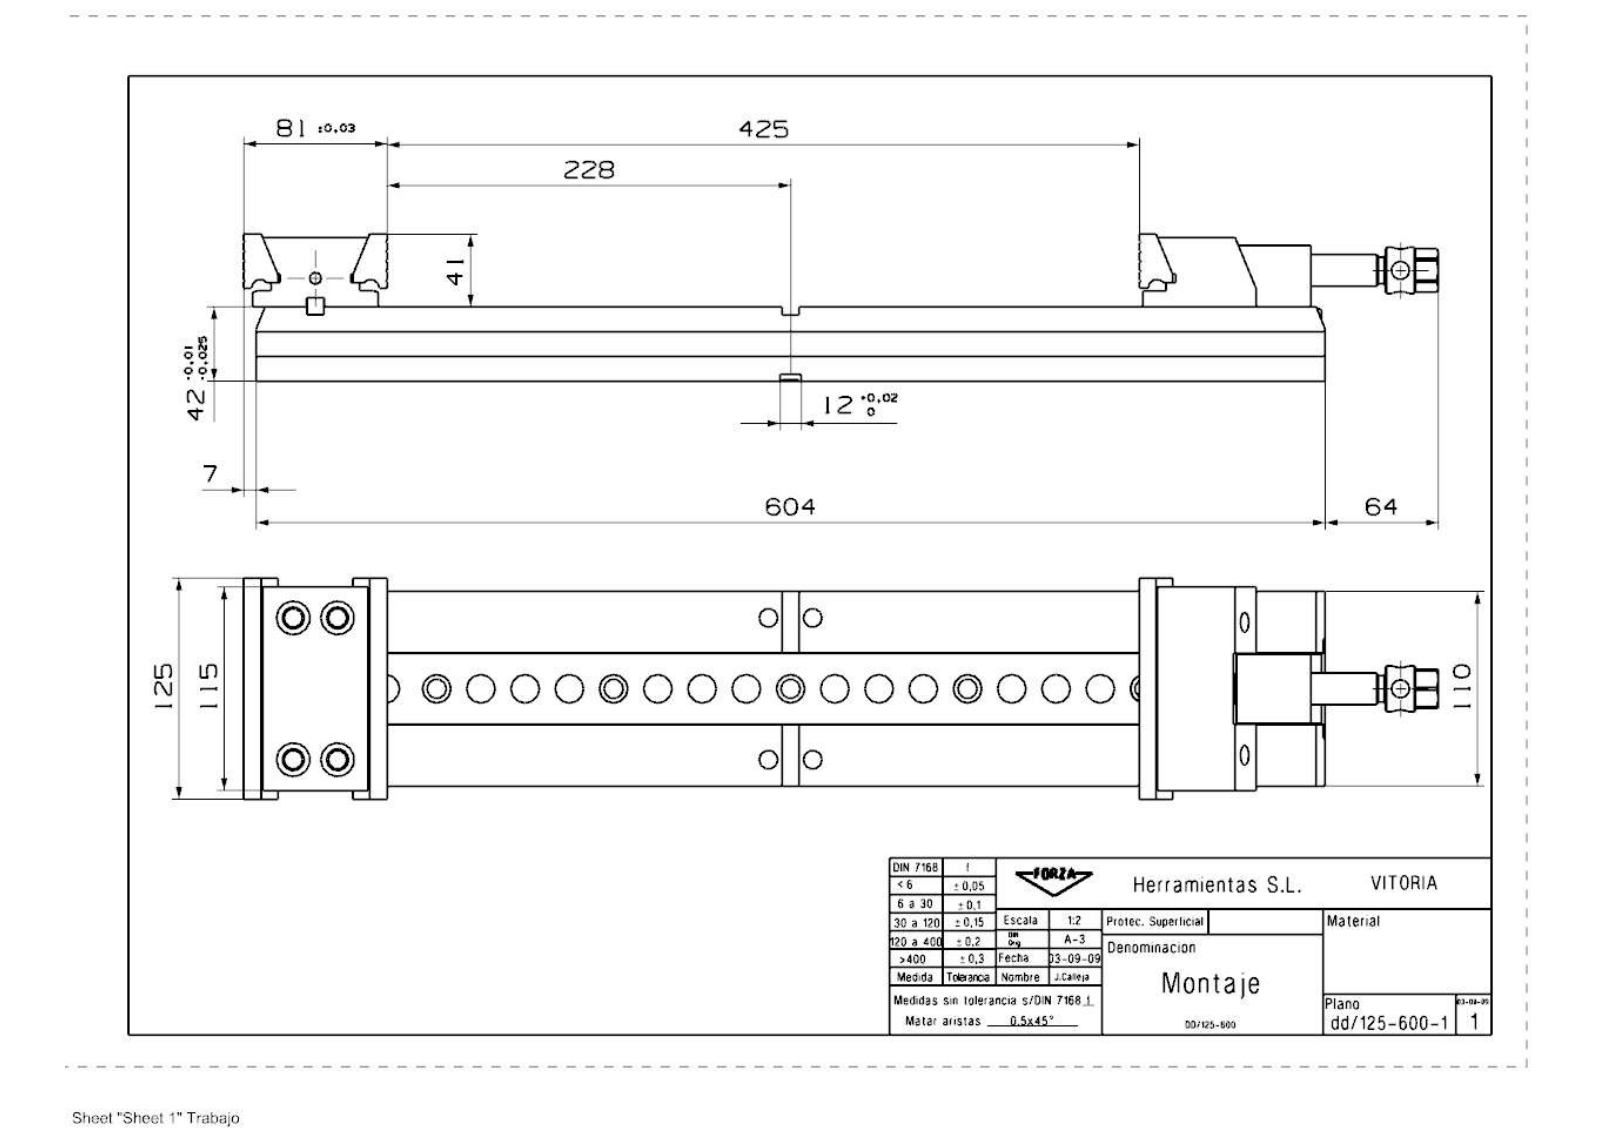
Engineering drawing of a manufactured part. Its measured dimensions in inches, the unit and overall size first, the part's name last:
Units: inches
Overall size (bounding box): 26.579 × 4.921 × 3.268
Round holes (diameter × count): ⌀0.417 ×8, ⌀0.433 ×7, ⌀0.63 ×5, ⌀0.204 ×4, ⌀0.275 ×4, ⌀0.295 ×4, ⌀0.492 ×4, ⌀0.748 ×4, ⌀0.167 ×2, ⌀0.256 ×2, ⌀0.276 ×2, ⌀0.315 ×2
Round bosses / shafts (diameter × count): ⌀1.024 ×1, ⌀0.698 ×1, ⌀0.591 ×1, ⌀0.571 ×1, ⌀0.413 ×1
Partial cylindrical surfaces — rounded edges, fillets, slot ends (radius × count): R0.012 ×10, R0.236 ×5, R0.157 ×4, R0.63 ×4, R0.197 ×3, R0.063 ×2, R0.394 ×2, R0.118 ×1
Main face-to-face distances: 1.654, 1.063, 3.268, 0.197, 0.622, 1.031, 0.551, 0.866, 4.134, 3.071
Hole centre spacings: 0.138, 0.453, 0.511, 0.799, 0.984, 1.65, 1.909, 2.047
Volume: 157.1 in³ · Surface area: 665.9 in²
Bodies: 12 solids, 554 faces (363 planar, 131 cylindrical, 60 other)
Part name (STEP PRODUCT): DD_125_600_Mordaza_Una
STEP written by: SIEMENS PLM Software NX 7.5 (AUTOMOTIVE_DESIGN)
